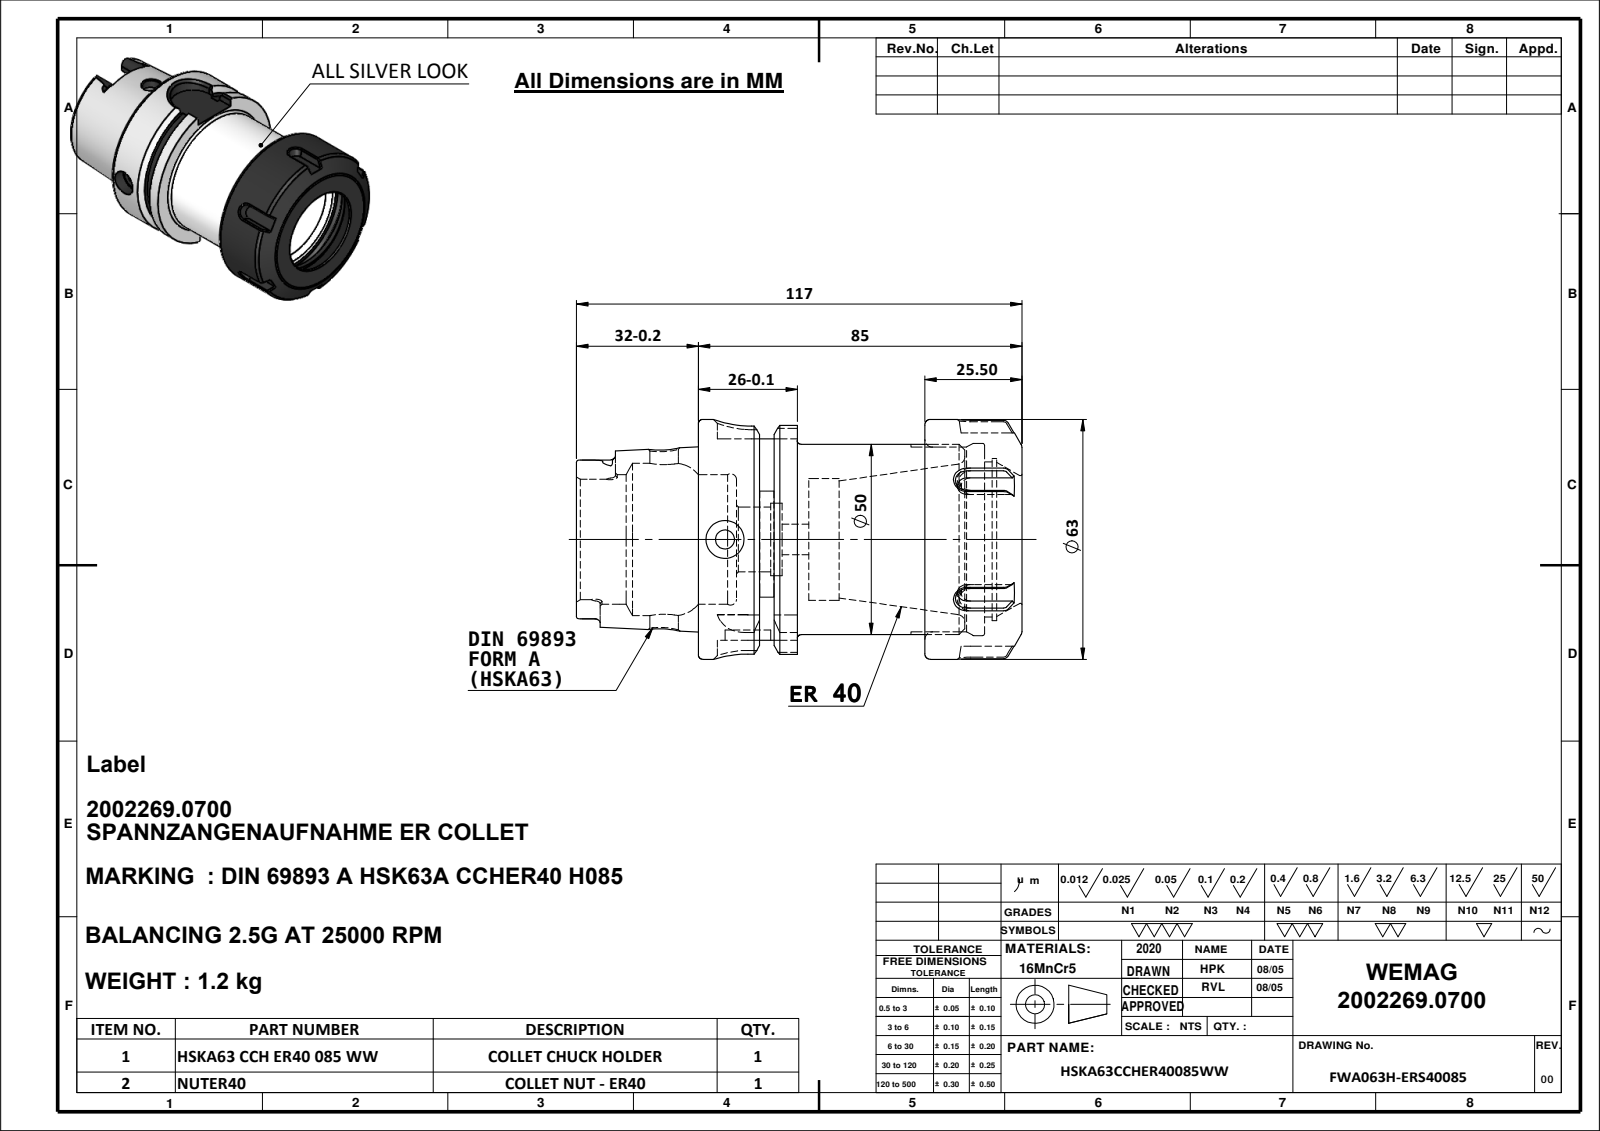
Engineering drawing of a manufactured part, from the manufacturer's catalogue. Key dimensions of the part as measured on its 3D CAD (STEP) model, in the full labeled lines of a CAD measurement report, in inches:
Part name (STEP PRODUCT): 9163A-ER840085
STEP written by: SolidWorks 2018 (AUTOMOTIVE_DESIGN)
Units: inches
Bodies: 1 solid, 155 faces (52 planar, 47 cylindrical, 56 other)
Overall size (bounding box): 4.016 × 2.48 × 2.48
Volume: 7.802 in³ · Surface area: 51.63 in²
Round holes (diameter × count): ⌀0.295 ×1, ⌀0.315 ×1, ⌀0.394 ×1, ⌀0.472 ×1, ⌀0.669 ×1, ⌀0.748 ×1, ⌀1.26 ×1, ⌀1.339 ×1, ⌀1.575 ×1
Round bosses / shafts (diameter × count): ⌀2.48 ×1, ⌀2.165 ×1, ⌀1.969 ×1
Partial cylindrical surfaces — rounded edges, fillets, slot ends (radius × count): R0.051 ×6, R0.113 ×4, R0.315 ×2, R0.354 ×1
Main face-to-face distances: 1.024, 0.118, 1.142, 0.394, 0.748, 0.63, 1.26, 1.654, 2.283, 2.402
Hole centre spacings: 0.866
